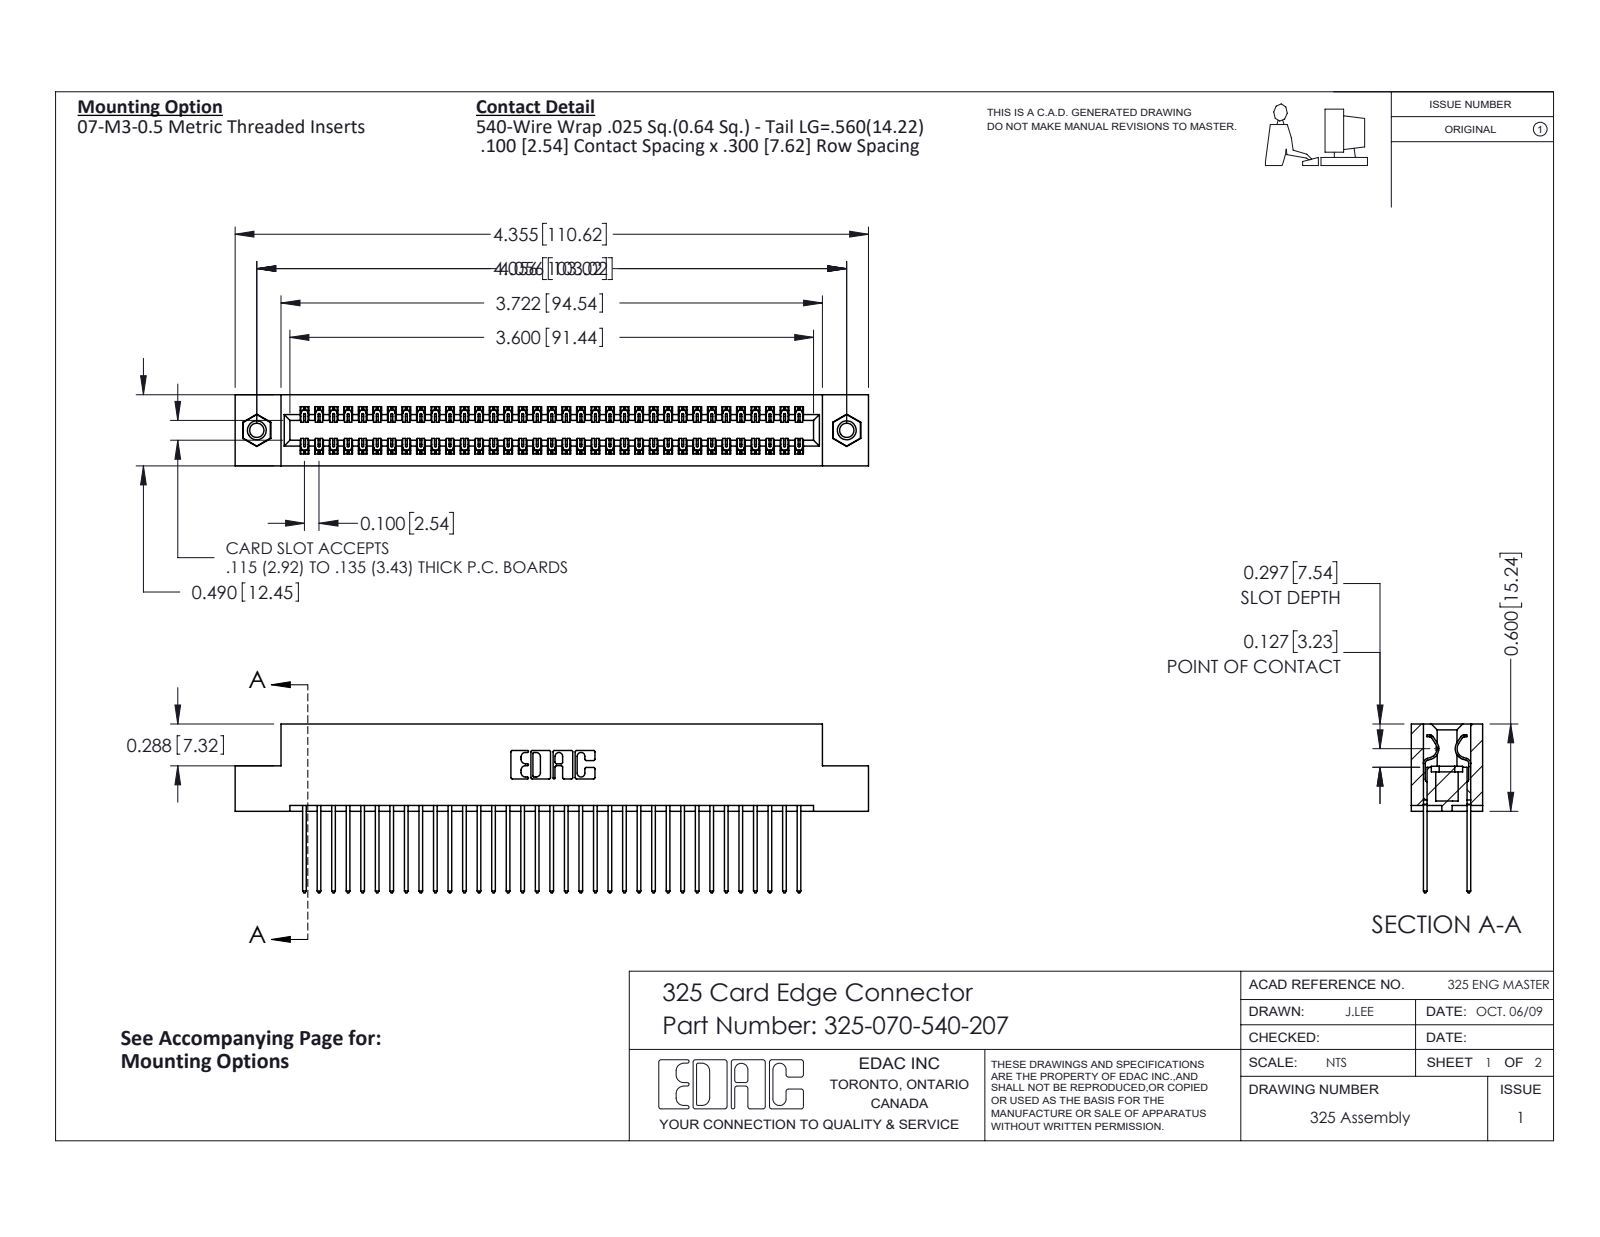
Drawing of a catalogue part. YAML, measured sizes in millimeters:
part_name: "325 Part_TI; 325-292-001_325-293-140; 345-250-001_345-250-005-103; 325-070-540-207"
step_written_by: "SolidWorks 2016 (CONFIG_CONTROL_DESIGN)"
units: millimeters
bodies: {solids: 73, faces: 3814, planar: 2622, cylindrical: 1176, other: 16}
overall_size: [110.6, 29.5, 12.4]
volume: 14500
surface_area: 18640
round_holes:
  - {diameter: 2.5, count: 2}
  - {diameter: 3.2, count: 2}
  - {diameter: 4.1, count: 2}
round_bosses_or_shafts:
  - {diameter: 3.9, count: 2}
partial_cylinders:
  - {radius: 0.2, count: 105}
  - {radius: 0.3, count: 70}
  - {radius: 0.3, count: 22}
  - {radius: 0.2, count: 6}
  - {radius: 0.8, count: 6}
  - {radius: 0.7, count: 3}
  - {radius: 0.4, count: 2}
  - {radius: 0.6, count: 2}
face_to_face_distances: [2.1, 10.3, 7.6, 2.7, 9.7, 0.6, 12.4, 8.3, 7, 14.2]
hole_center_spacings: [103]
